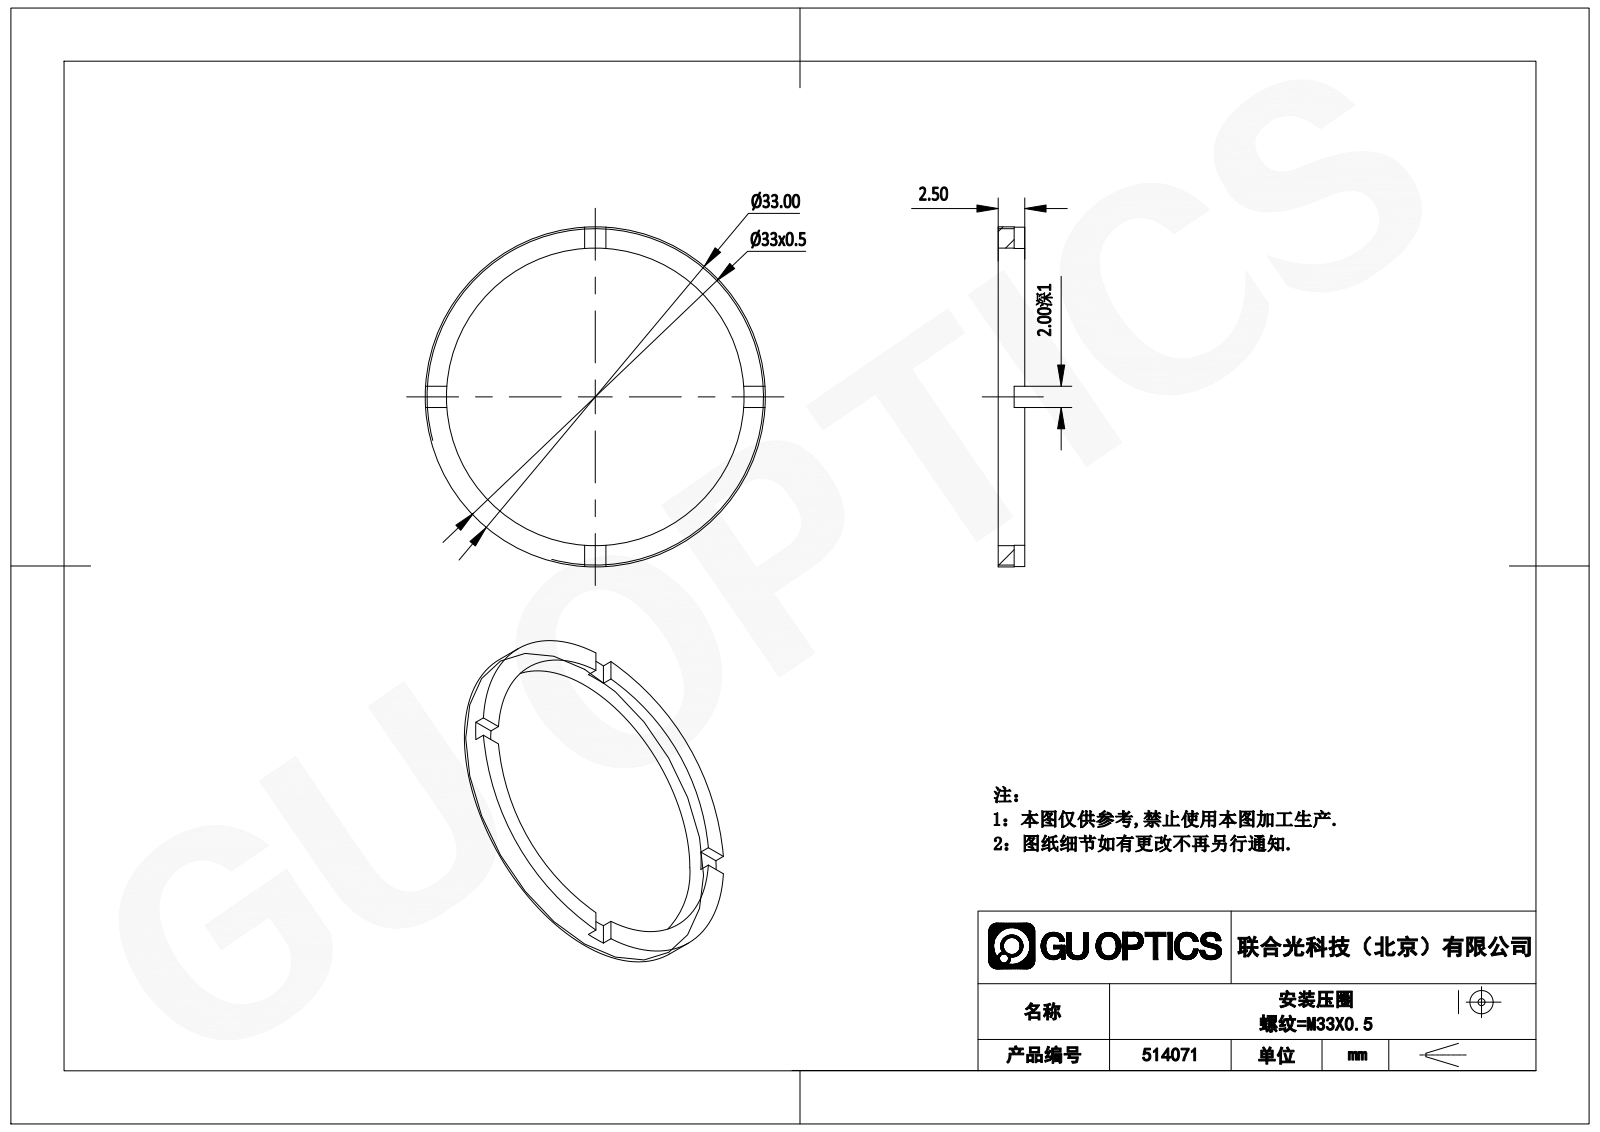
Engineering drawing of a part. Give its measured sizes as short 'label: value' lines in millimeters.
name: 514071
written by: SolidWorks 2020 (CONFIG_CONTROL_DESIGN)
unit: mm
bodies: 1 solid, 21 faces (17 planar, 4 cylindrical, 0 other)
size: 33 × 33 × 2.5
volume: 471 mm³; area: 877 mm²
holes: 1× ⌀29
bosses: 1× ⌀33
face distances: 2.5, 1.5, 1, 2
